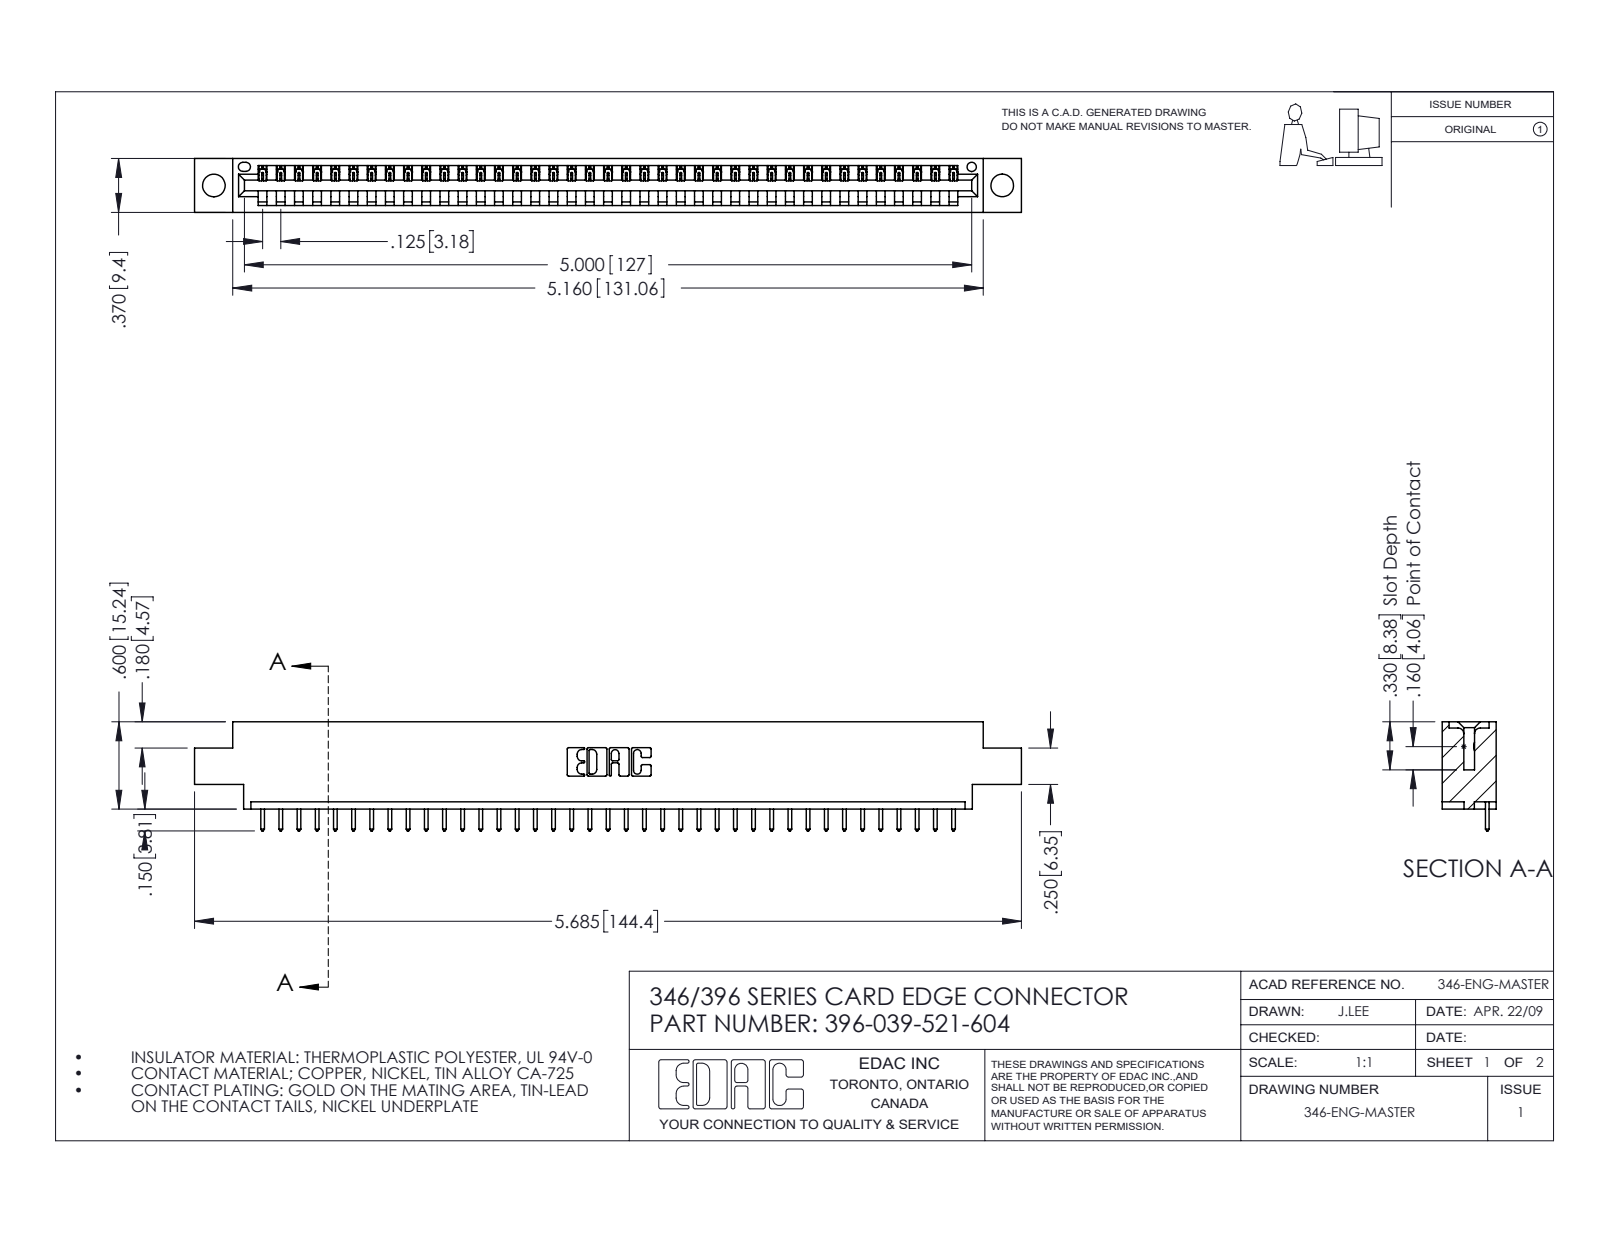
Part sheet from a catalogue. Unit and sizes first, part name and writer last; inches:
Units: inches
Overall size (bounding box): 5.685 × 0.75 × 0.37
Round holes (diameter × count): ⌀0.156 ×2, ⌀0.064 ×1
Partial cylindrical surfaces — rounded edges, fillets, slot ends (radius × count): R0.006 ×78, R0.01 ×78, R0.01 ×22, R0.007 ×6, R0.031 ×6, R0.026 ×3, R0.031 ×2, R0.04 ×2
Main face-to-face distances: 0.048, 0.322, 0.37, 0.25, 0.072, 0.298, 0.025, 0.148, 0.222, 0.1
Hole centre spacings: 0.246, 5.211, 5.42
Volume: 0.821 in³ · Surface area: 25.26 in²
Bodies: 40 solids, 2388 faces (1640 planar, 748 cylindrical, 0 other)
Part name (STEP PRODUCT): 346 Part_0.170 Offset - 0.156 Dia-TH; 396-039-521-604; 345-292-001_345-293-121
STEP written by: SolidWorks 2016 (CONFIG_CONTROL_DESIGN)
